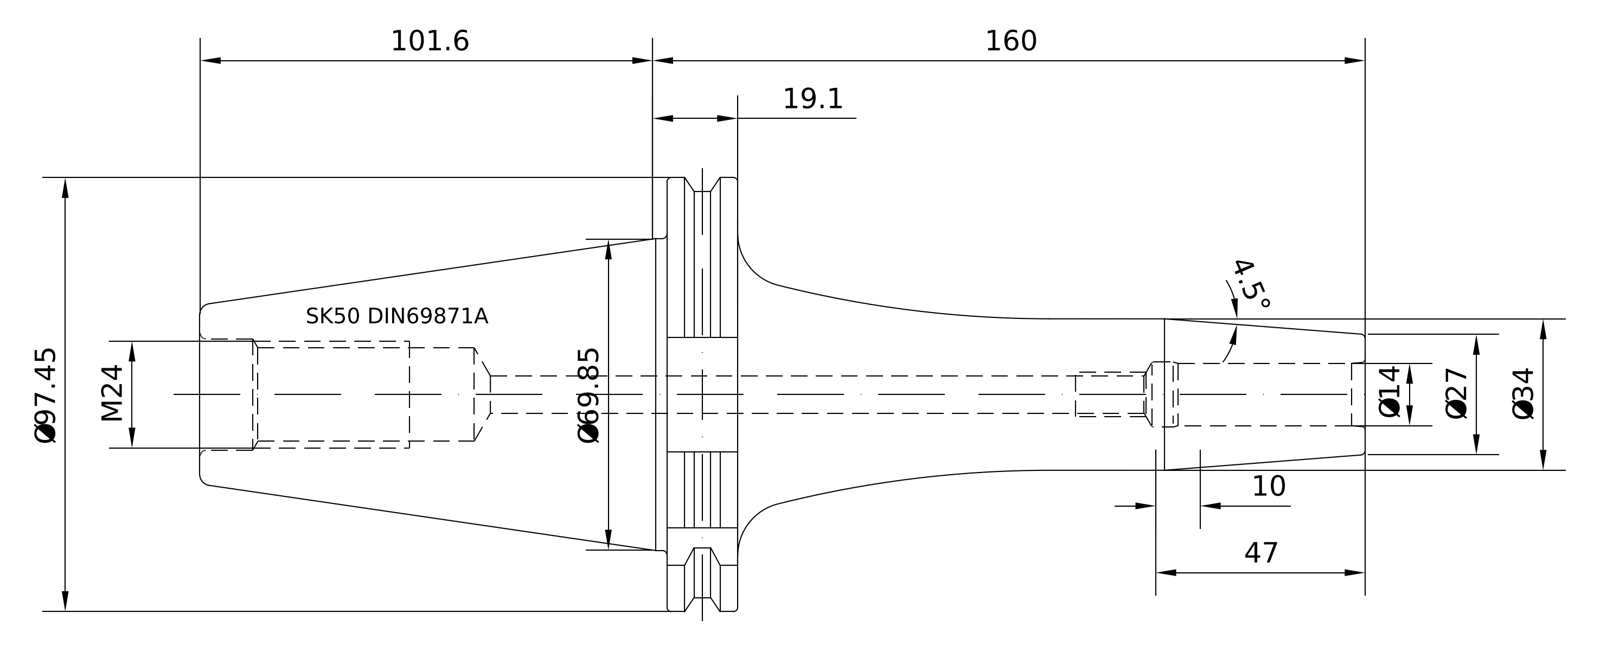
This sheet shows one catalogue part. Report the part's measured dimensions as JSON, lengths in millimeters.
{"part_name": "50-442-14", "step_written_by": "PRO/ENGINEER BY PARAMETRIC TECHNOLOGY CORPORATION, 2010430 (CONFIG_CONTROL_DESIGN)", "units": "millimeters", "bodies": {"solids": 1, "faces": 95, "planar": 21, "cylindrical": 24, "other": 50}, "overall_size": [261.6, 97.47, 94], "volume_mm3": 484303, "surface_area_mm2": 58719, "round_holes": [[14, 1], [20.75, 1], [25.01, 1], [25.7, 1]], "round_bosses_or_shafts": [[91, 1], [69.15, 1], [34, 1], [24.01, 1]], "partial_cylinders_radius": [[1.75, 1], [48.74, 1]], "face_to_face_distances": [15.85, 72.8, 104.8, 120.65, 261.6, 156.8, 140.95, 25.8, 214.6, 109.8]}
